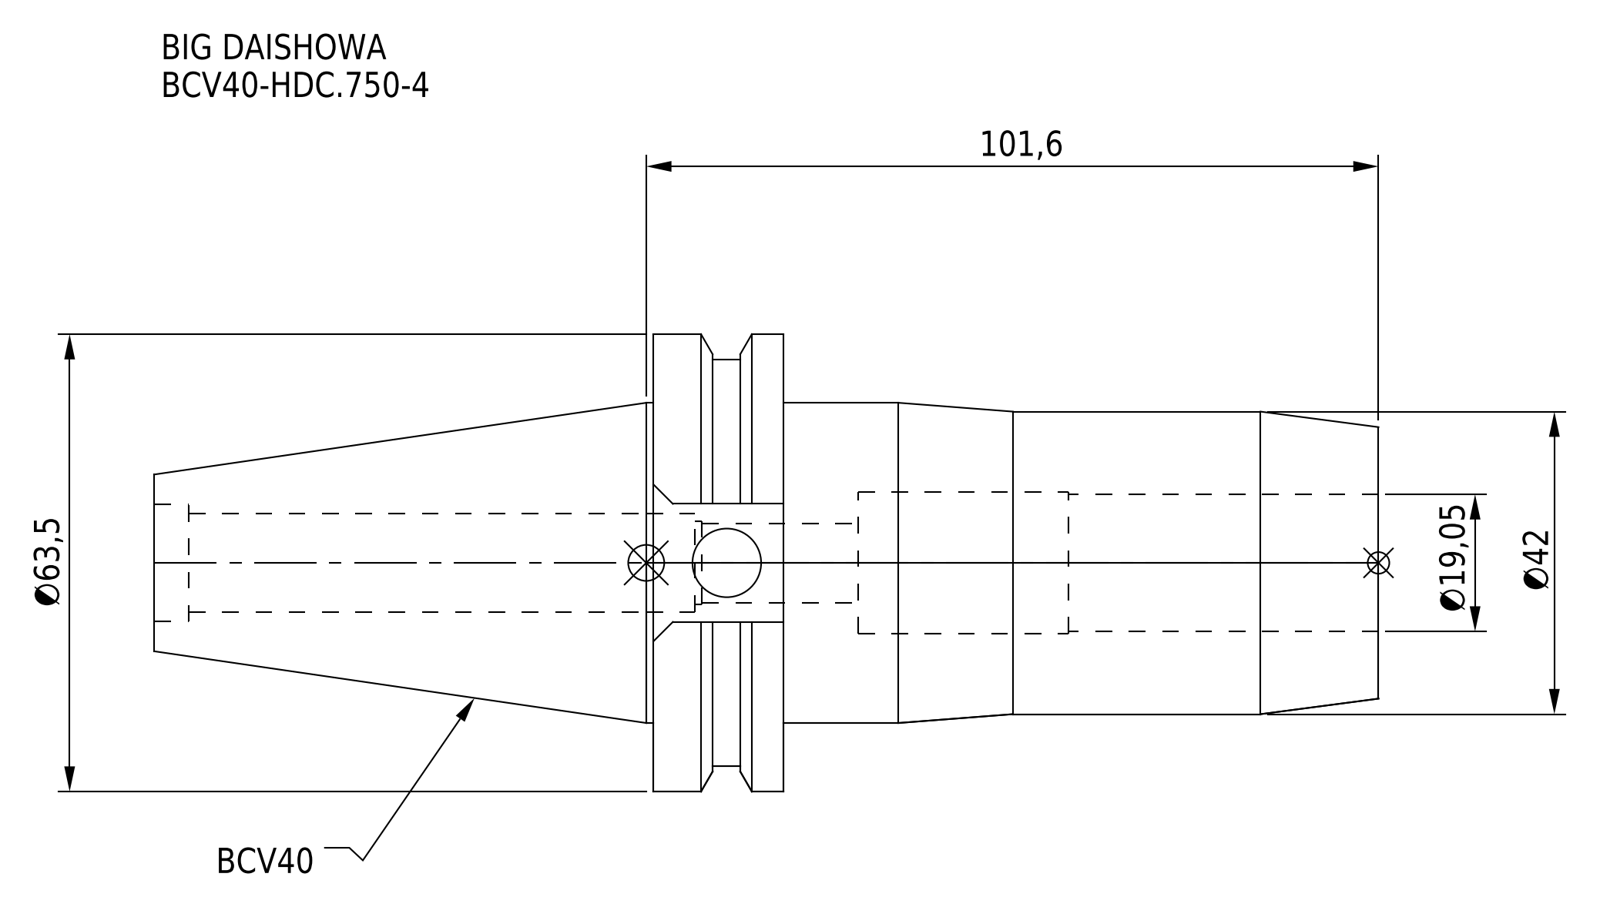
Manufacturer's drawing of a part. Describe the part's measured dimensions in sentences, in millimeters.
The part is named "BCV40-HDC_750-4". Its 3-D file was written by "CREO PARAMETRIC BY PTC INC, 2016380 (AUTOMOTIVE_DESIGN)". It is 1 solid with 62 faces: 24 planar, 28 cylindrical and 10 other. Overall it measures 169.85 by 63.5 by 61.35 millimeters. Its volume is 198 456 cubic millimeters and its surface area 35 772 square millimeters. Round holes: 1 of diameter 9.53, 1 of diameter 11, 1 of diameter 11.5, 1 of diameter 13.6, 1 of diameter 16.32, 1 of diameter 19.05, 1 of diameter 19.6. Round bosses or shafts: 1 of diameter 63.5, 1 of diameter 56.36, 1 of diameter 44.45, 1 of diameter 42. The main face-to-face distances are 18.05, 82.55, 100.6, 169.85, 87.3, 69.25, 47.55, 72.2, 10.35, 28.4.
